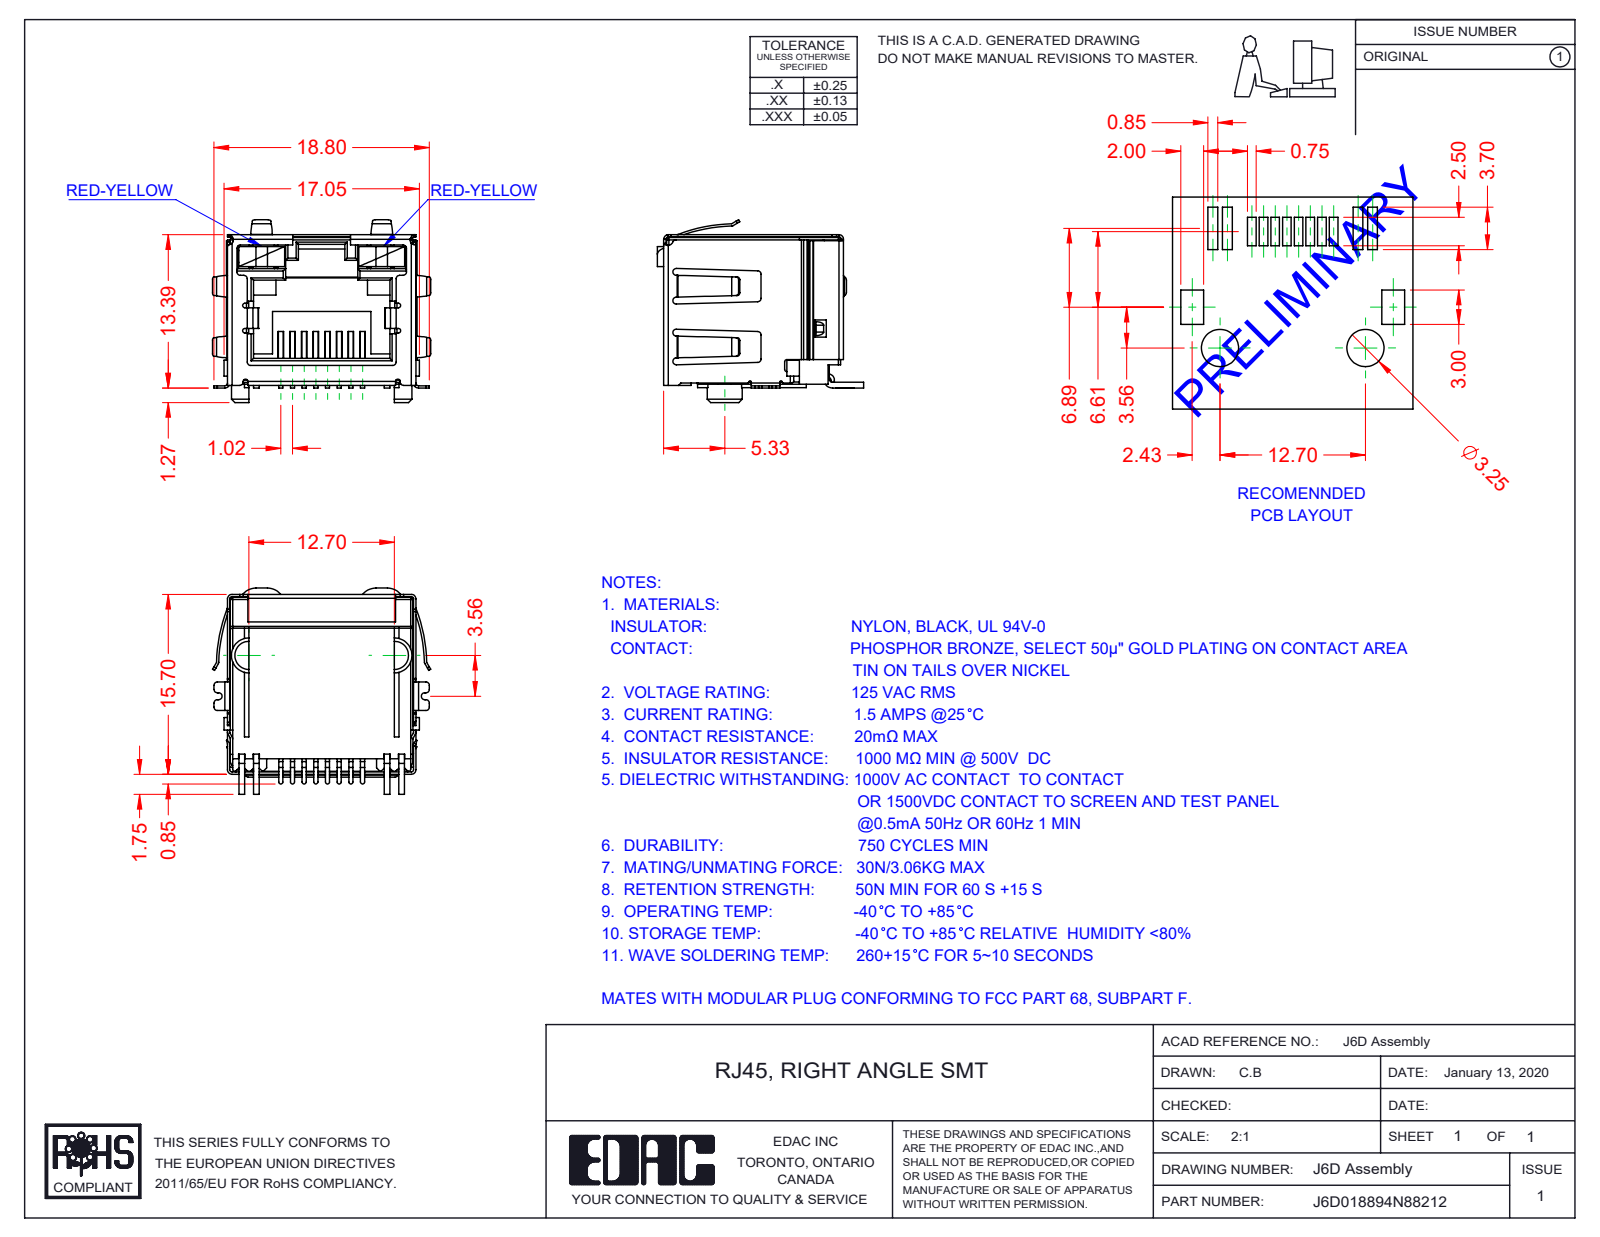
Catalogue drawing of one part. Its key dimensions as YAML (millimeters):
part_name: "6D LED LH_8-Red-Yellow; J6D018894N88212; 6D Insulator; 6D LED RH_8-Red-Yellow (+2 more)"
step_written_by: "SolidWorks 2016 (CONFIG_CONTROL_DESIGN)"
units: millimeters
bodies: {solids: 12, faces: 1034, planar: 703, cylindrical: 286, other: 45}
overall_size: [19.06, 18, 15.95]
volume: 1790
surface_area: 4796
partial_cylinders:
  - {radius: 0.3, count: 55}
  - {radius: 0.2, count: 40}
  - {radius: 0.4, count: 19}
  - {radius: 0.25, count: 16}
  - {radius: 0.1, count: 12}
  - {radius: 0.15, count: 8}
  - {radius: 0.18, count: 8}
  - {radius: 0.5, count: 6}
face_to_face_distances: [16, 16.2, 16.25, 2.25, 1, 15.95, 12.8, 0.45, 13.05, 10.6]
